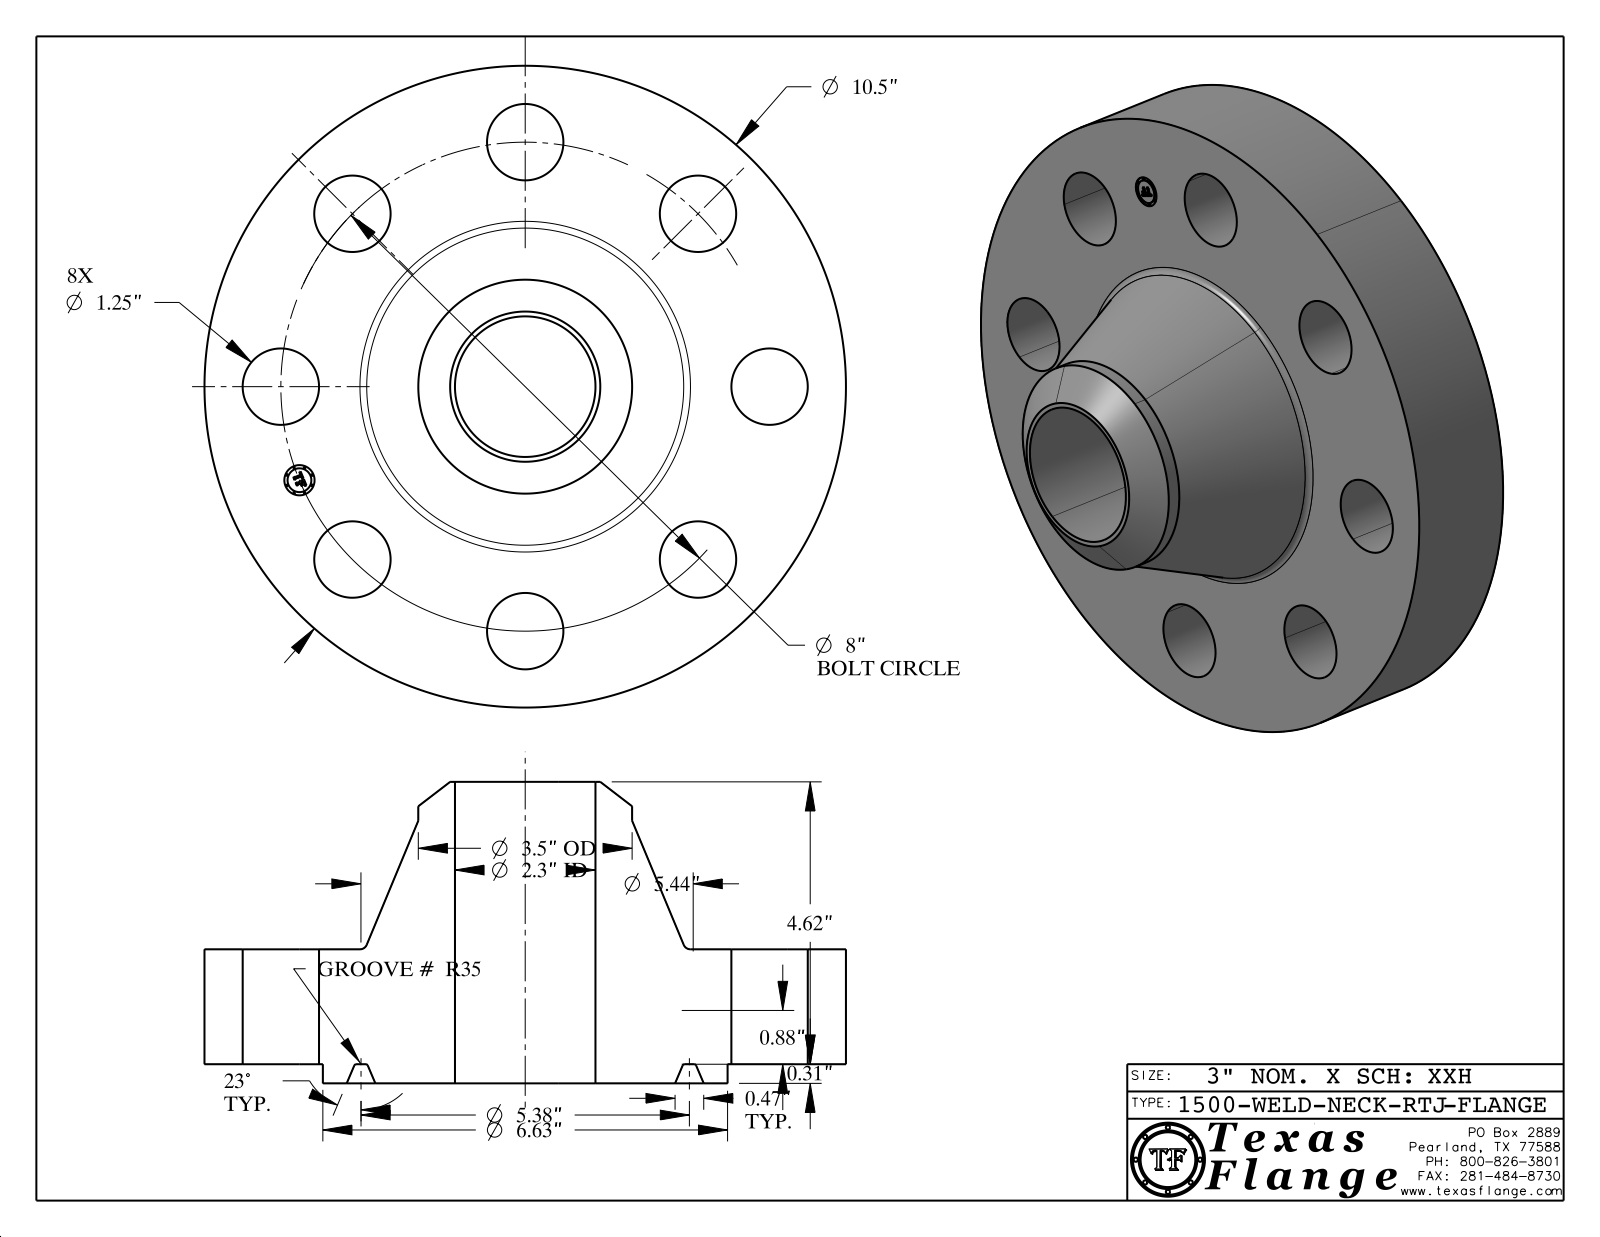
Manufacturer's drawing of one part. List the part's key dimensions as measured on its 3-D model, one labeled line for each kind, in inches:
Part name (STEP PRODUCT): 1500-WELD-NECK-RTJ
STEP written by: CATIA V5 STEP AP214 (AUTOMOTIVE_DESIGN)
Units: inches
Bodies: 1 solid, 429 faces (371 planar, 44 cylindrical, 14 other)
Overall size (bounding box): 10.5 × 10.5 × 4.933
Volume: 170 in³ · Surface area: 338.2 in²
Round holes (diameter × count): ⌀1.25 ×8, ⌀0.495 ×1, ⌀2.3 ×1
Round bosses / shafts (diameter × count): ⌀0.03 ×8, ⌀10.5 ×1, ⌀6.625 ×1, ⌀3.5 ×1, ⌀0.39 ×1
Main face-to-face distances: 1.88, 0.313, 2.193, 4.933, 4.62, 2.74, 0.015, 2.178, 1.865, 2.755
Hole centre spacings: 4, 3.061, 5.657, 7.391, 1.561, 6.652, 7.846, 8
